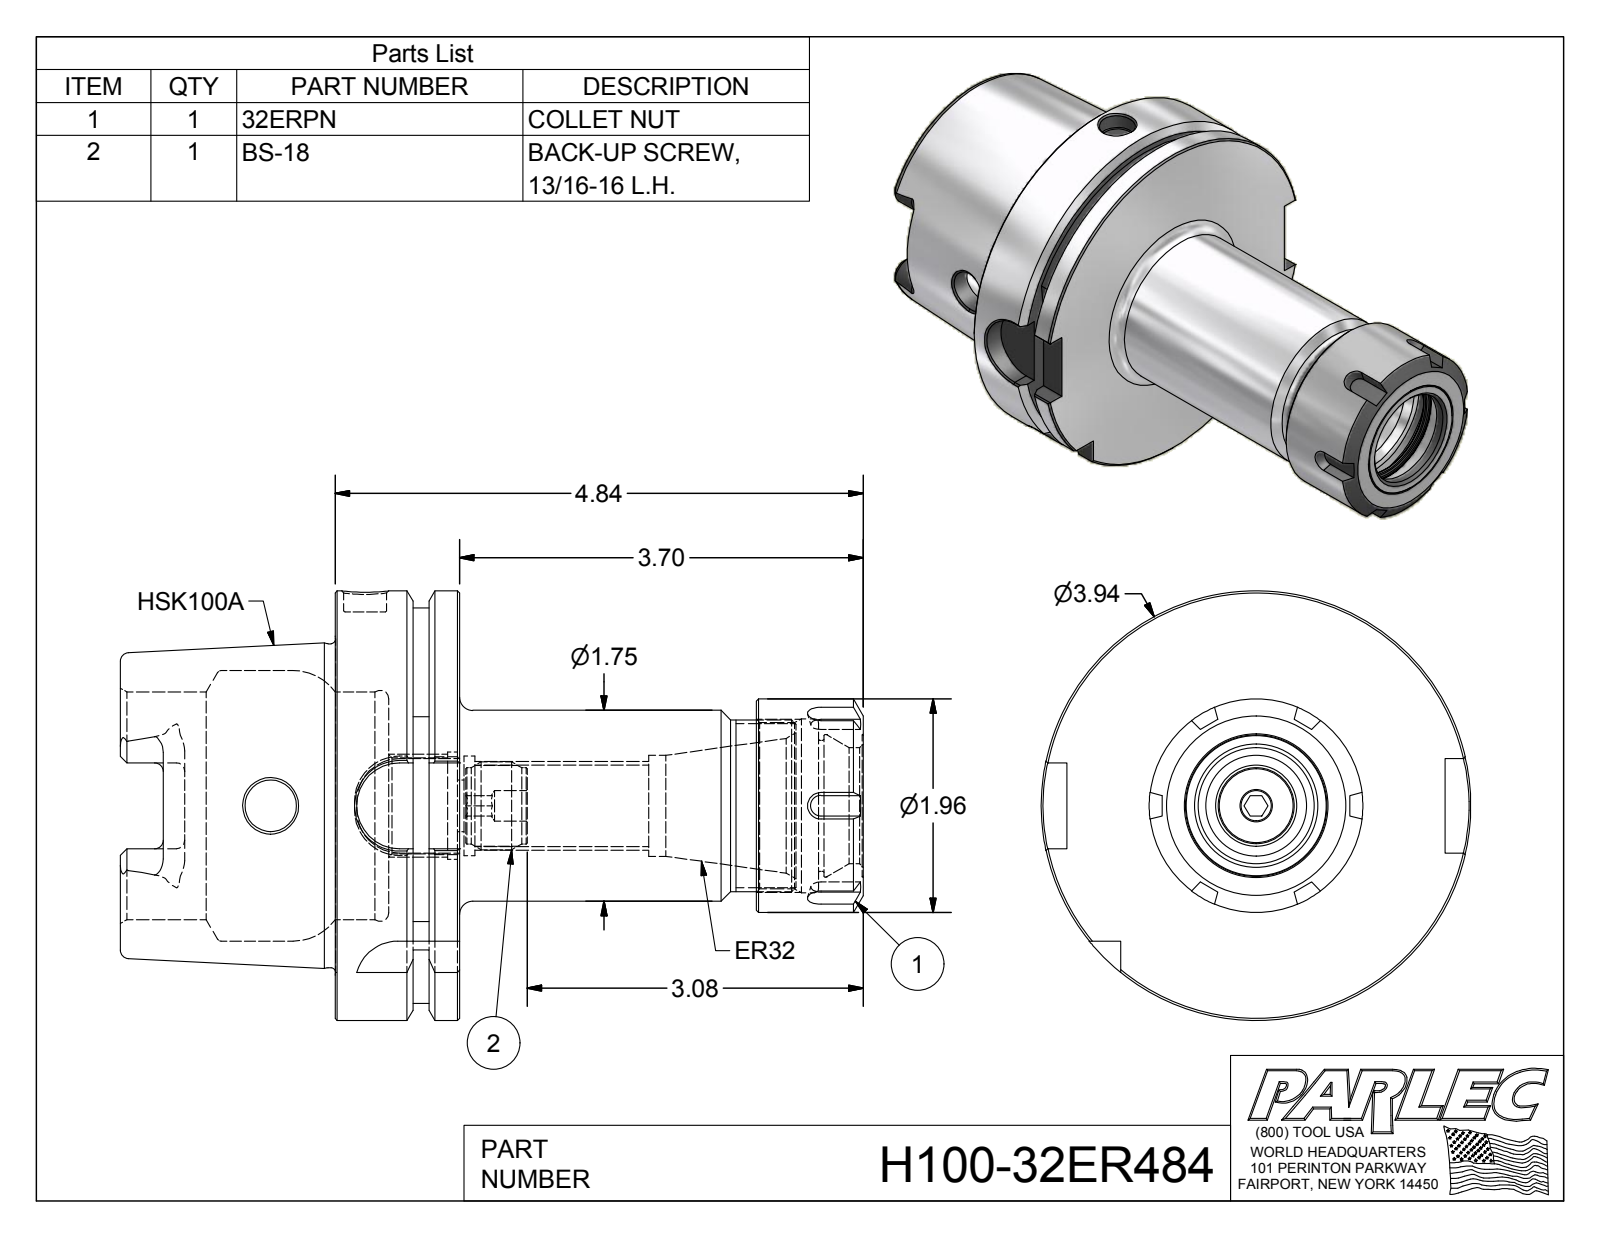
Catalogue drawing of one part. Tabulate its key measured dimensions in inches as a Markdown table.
| quantity | value |
| --- | --- |
| part name | H100-32ER484; H100-32ER5-1; BS-18; 32ERPN |
| STEP written by | Autodesk Inventor 2012 (AUTOMOTIVE_DESIGN) |
| units | inches |
| bodies | 3 solids, 197 faces (76 planar, 46 cylindrical, 75 other) |
| overall size | 6.809 × 3.937 × 3.937 |
| volume | 22.18 in³ |
| surface area | 118.7 in² |
| round holes (diameter × count) | 0.472 × 2, 0.28 × 1, 0.394 × 1, 0.745 × 1, 0.881 × 1, 0.912 × 1, 0.925 × 1, 0.985 × 1, 1.063 × 1, 1.2 × 1, 1.305 × 1, 1.523 × 1 |
| round bosses / shafts (diameter × count) | 3.937 × 1, 2.967 × 1, 1.958 × 1, 1.75 × 1, 1.575 × 1, 0.805 × 1, 0.7 × 1 |
| partial cylindrical surfaces (radius × count) | 0.079 × 6, 0.192 × 4, 0.394 × 4, 1.811 × 1 |
| main face-to-face distances | 1.142, 0.492, 0.65, 1.969, 2.461, 3.11, 6.809, 4.84, 4.348, 3.698 |
